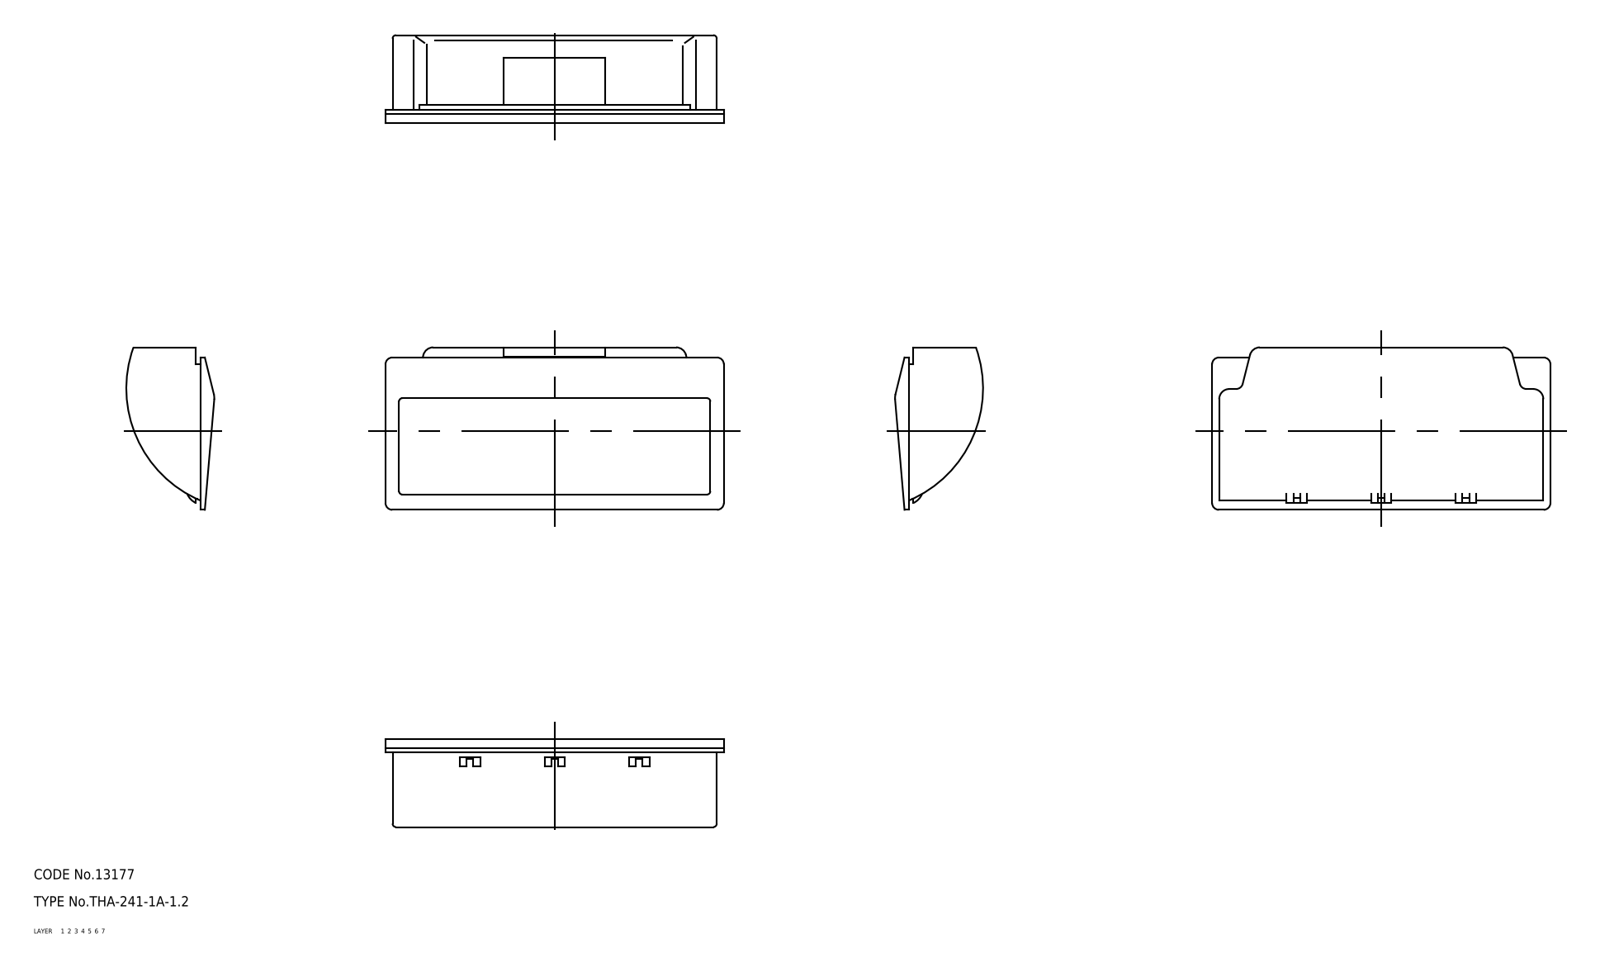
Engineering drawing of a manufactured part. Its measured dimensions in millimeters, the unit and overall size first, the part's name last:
Units: millimetres
Overall size (bounding box): 100 × 48 × 26
Volume: 24 203 mm³ · Surface area: 19 845 mm²
Bodies: 1 solid, 106 faces (0 planar, 0 cylindrical, 106 other)
Part name (STEP PRODUCT): pull
STEP written by: CADfix (AUTOMOTIVE_DESIGN)
